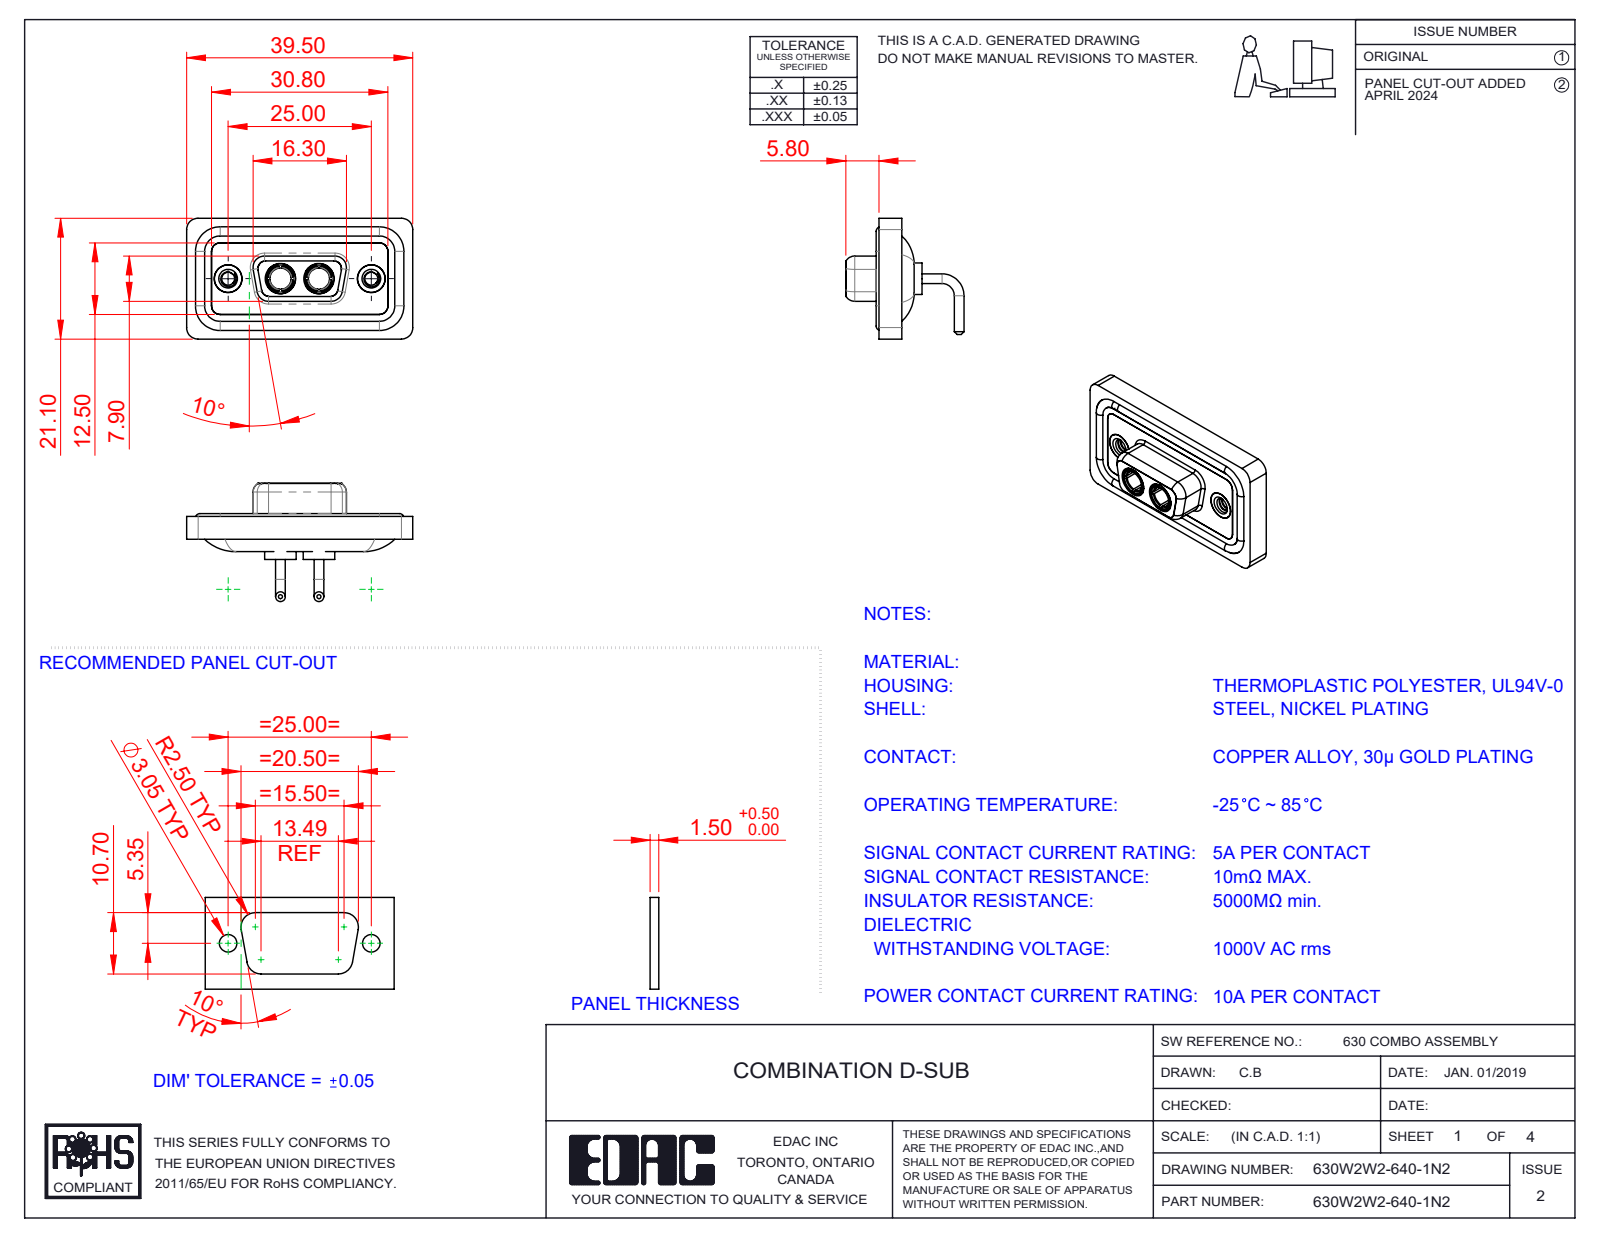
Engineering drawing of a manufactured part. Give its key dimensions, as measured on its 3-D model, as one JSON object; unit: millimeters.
{"part_name": "630Combo Shell Rear_09 Contacts; Power Socket_10A RA; 630Combo Threaded Rivet_2; 630Combo Waterproof Housing_09 Contacts (+3 more)", "step_written_by": "SolidWorks 2023 (CONFIG_CONTROL_DESIGN)", "units": "millimeters", "bodies": {"solids": 11, "faces": 542, "planar": 163, "cylindrical": 238, "other": 141}, "overall_size": [39.5, 21.1, 20.65], "volume_mm3": 4700, "surface_area_mm2": 7684, "round_holes": [[4.85, 4], [2.26, 2], [3.7, 2], [4, 2], [4.05, 2], [5, 2], [5.3, 2]], "round_bosses_or_shafts": [[1.7, 4], [1.6, 4], [5.5, 2], [5.2, 2], [4.96, 2], [4.95, 2], [4.8, 2], [4.75, 2]], "partial_cylinders_radius": [[1.5, 18], [2, 18], [1.35, 8], [1.6, 8], [0.25, 4], [0.5, 4], [0.6, 4], [0.65, 4]], "face_to_face_distances": [0.4, 1.8, 1.1, 2.9, 2.5, 1.6, 3.1, 1.5, 2.1, 0.5], "hole_center_spacings": [9.14, 15.86, 6.72, 25]}
